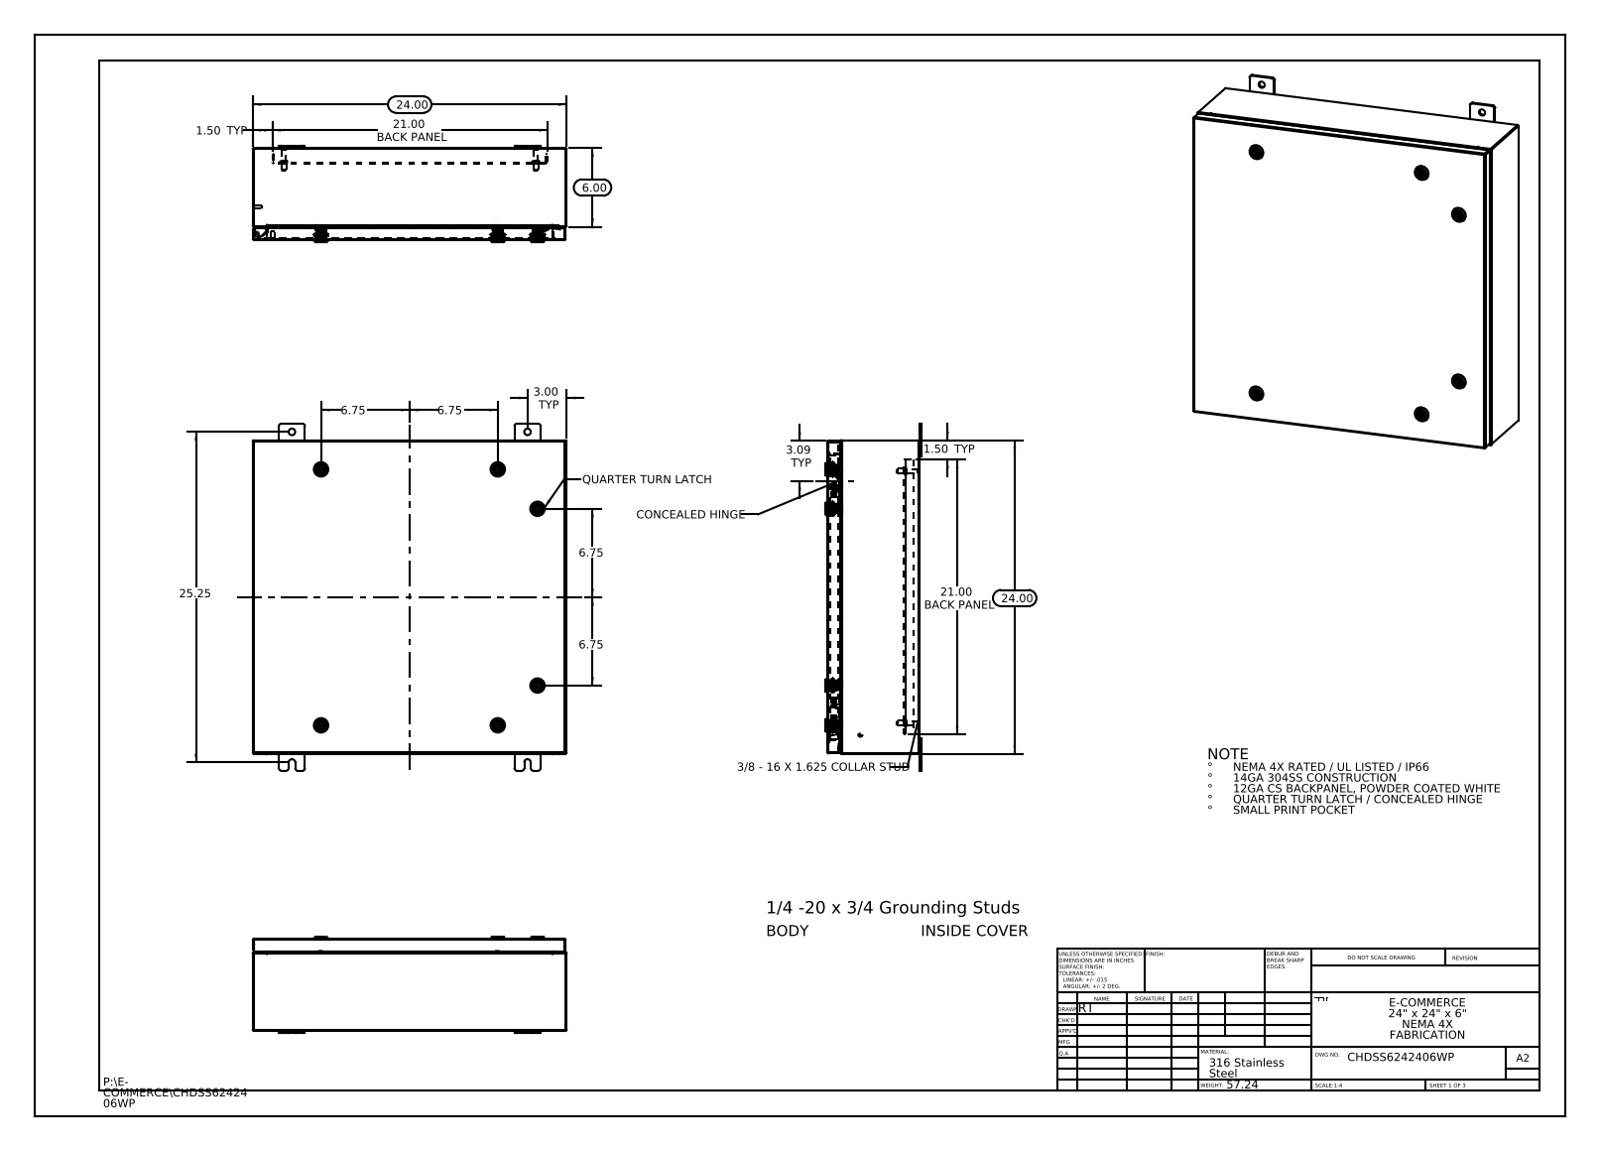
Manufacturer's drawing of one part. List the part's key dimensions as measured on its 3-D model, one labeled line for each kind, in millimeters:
Part name (STEP PRODUCT): CHDSS6242406WP Backpanel; CHDSS6242406WP Body; Concealed Hinge (Cover Side); CHDSS6242406WP Mounting Studs (+8 more)
STEP written by: SolidWorks 2013 (CONFIG_CONTROL_DESIGN)
Units: millimetres
Bodies: 55 solids, 5420 faces (1592 planar, 1692 cylindrical, 2136 other)
Overall size (bounding box): 673.1 × 609.6 × 186.8
Volume: 3 350 000 mm³ · Surface area: 3 271 000 mm²
Round holes (diameter × count): ⌀12.7 ×8, ⌀5 ×6, ⌀10 ×6, ⌀10.2 ×6, ⌀16 ×6, ⌀20 ×6, ⌀3.5 ×4, ⌀5.4 ×1
Round bosses / shafts (diameter × count): ⌀6 ×8, ⌀28 ×6, ⌀19.8 ×6, ⌀15.9 ×6, ⌀15.5 ×6, ⌀13.5 ×6, ⌀10 ×6, ⌀2.9 ×6
Partial cylindrical surfaces — rounded edges, fillets, slot ends (radius × count): R0.2 ×198, R3 ×198, R0.7 ×72, R0.5 ×24, R4.8 ×24, R5 ×24, R0.3 ×20, R2.2 ×18
Main face-to-face distances: 1.9, 1.9, 178.1, 176.1, 176.2, 174.3, 607.7, 2.6, 25.4, 27.3
Hole centre spacings: 342.9, 17.5, 47.2, 73.1, 77.9, 416, 427.1, 449.2
